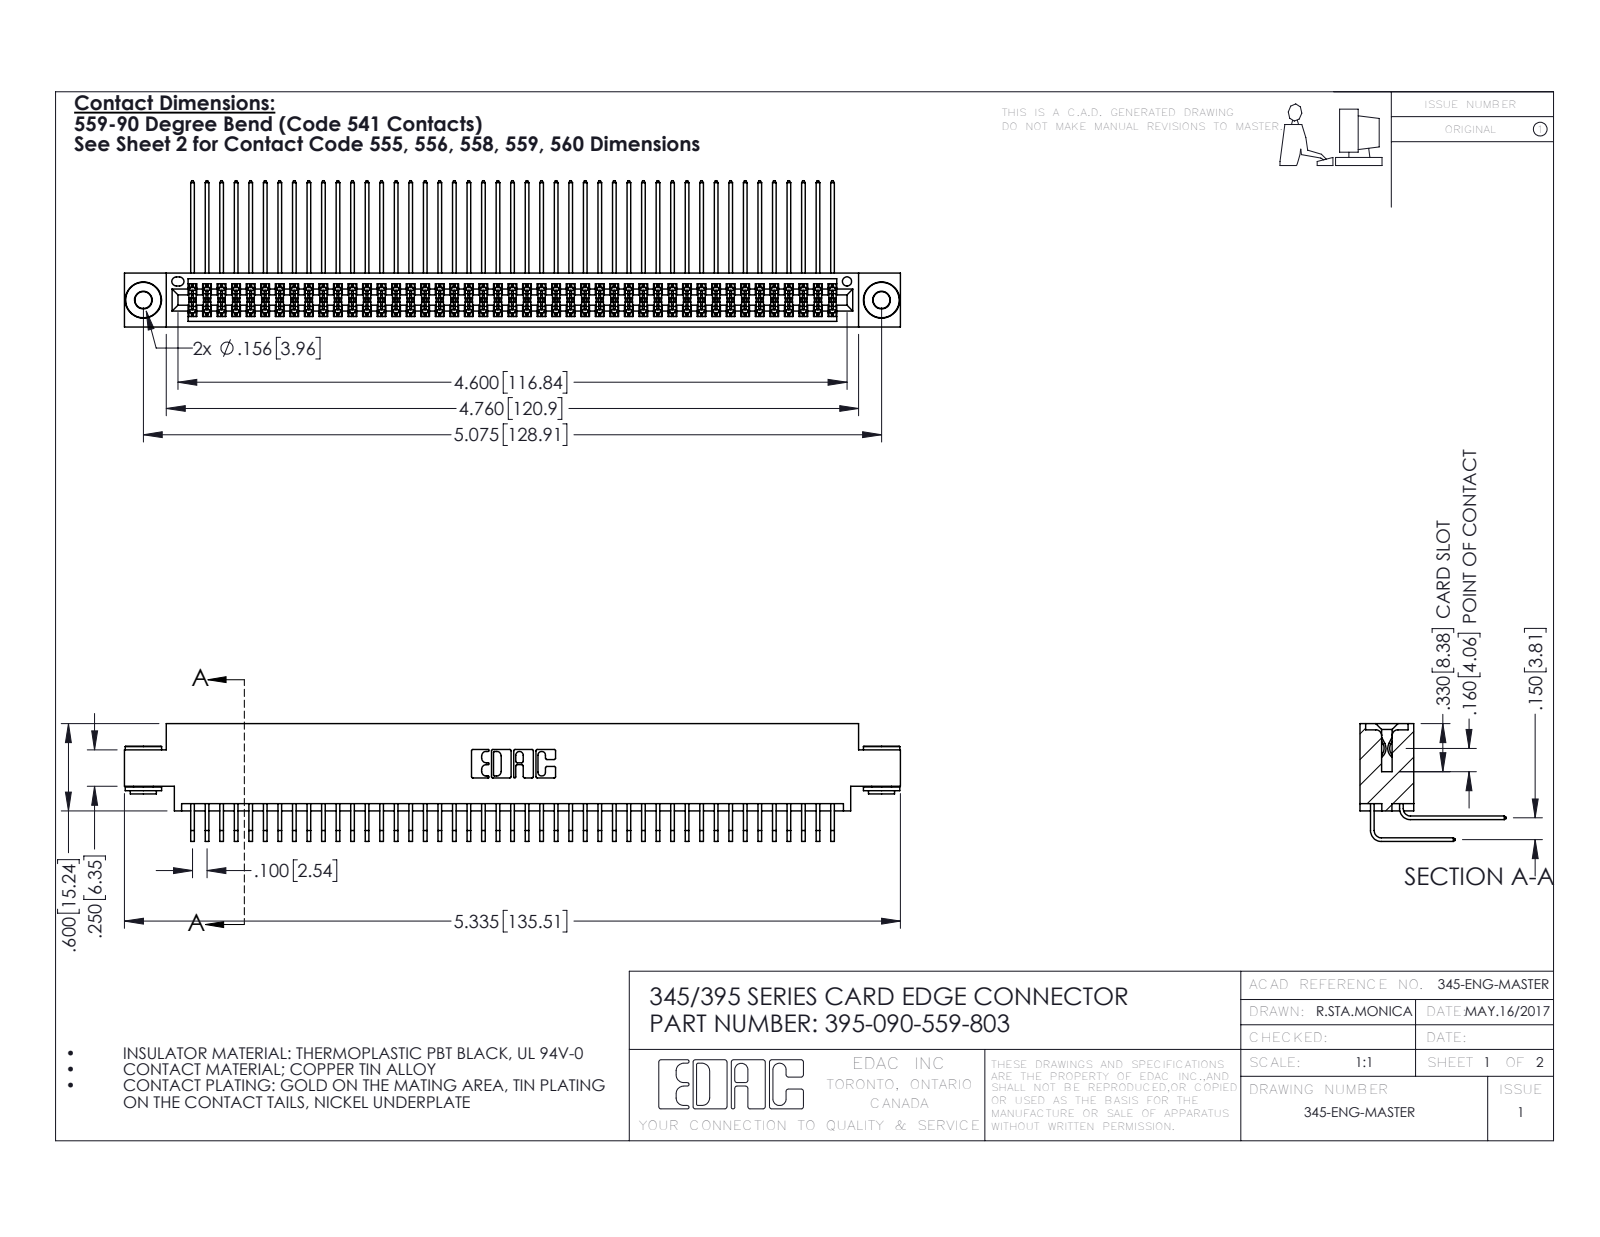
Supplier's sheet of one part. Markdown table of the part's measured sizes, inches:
| quantity | value |
| --- | --- |
| part name | 345-292-001_558 559 Tail - 1; 395-090-559-803; 345-250-002_345-250-002-102; 345 Part_0.170 Offset - 0.156 Dia-TH (+1 more) |
| STEP written by | SolidWorks 2016 (CONFIG_CONTROL_DESIGN) |
| units | inches |
| bodies | 93 solids, 4848 faces (3244 planar, 1596 cylindrical, 8 other) |
| overall size | 5.335 × 1.005 × 0.809 |
| volume | 0.831 in³ |
| surface area | 35.61 in² |
| round holes (diameter × count) | 0.116 × 2, 0.156 × 2, 0.064 × 1 |
| round bosses / shafts (diameter × count) | 0.25 × 2, 0.18 × 2, 0.136 × 2 |
| partial cylindrical surfaces (radius × count) | 0.006 × 135, 0.01 × 22, 0.007 × 6, 0.031 × 6, 0.026 × 3, 0.014 × 2, 0.019 × 2, 0.022 × 2 |
| main face-to-face distances | 0.072, 0.298, 0.37, 0.2, 0.098, 0.272, 0.025, 0.175, 0.225, 0.15 |
| hole center spacings | 0.27, 4.839, 5.075 |
